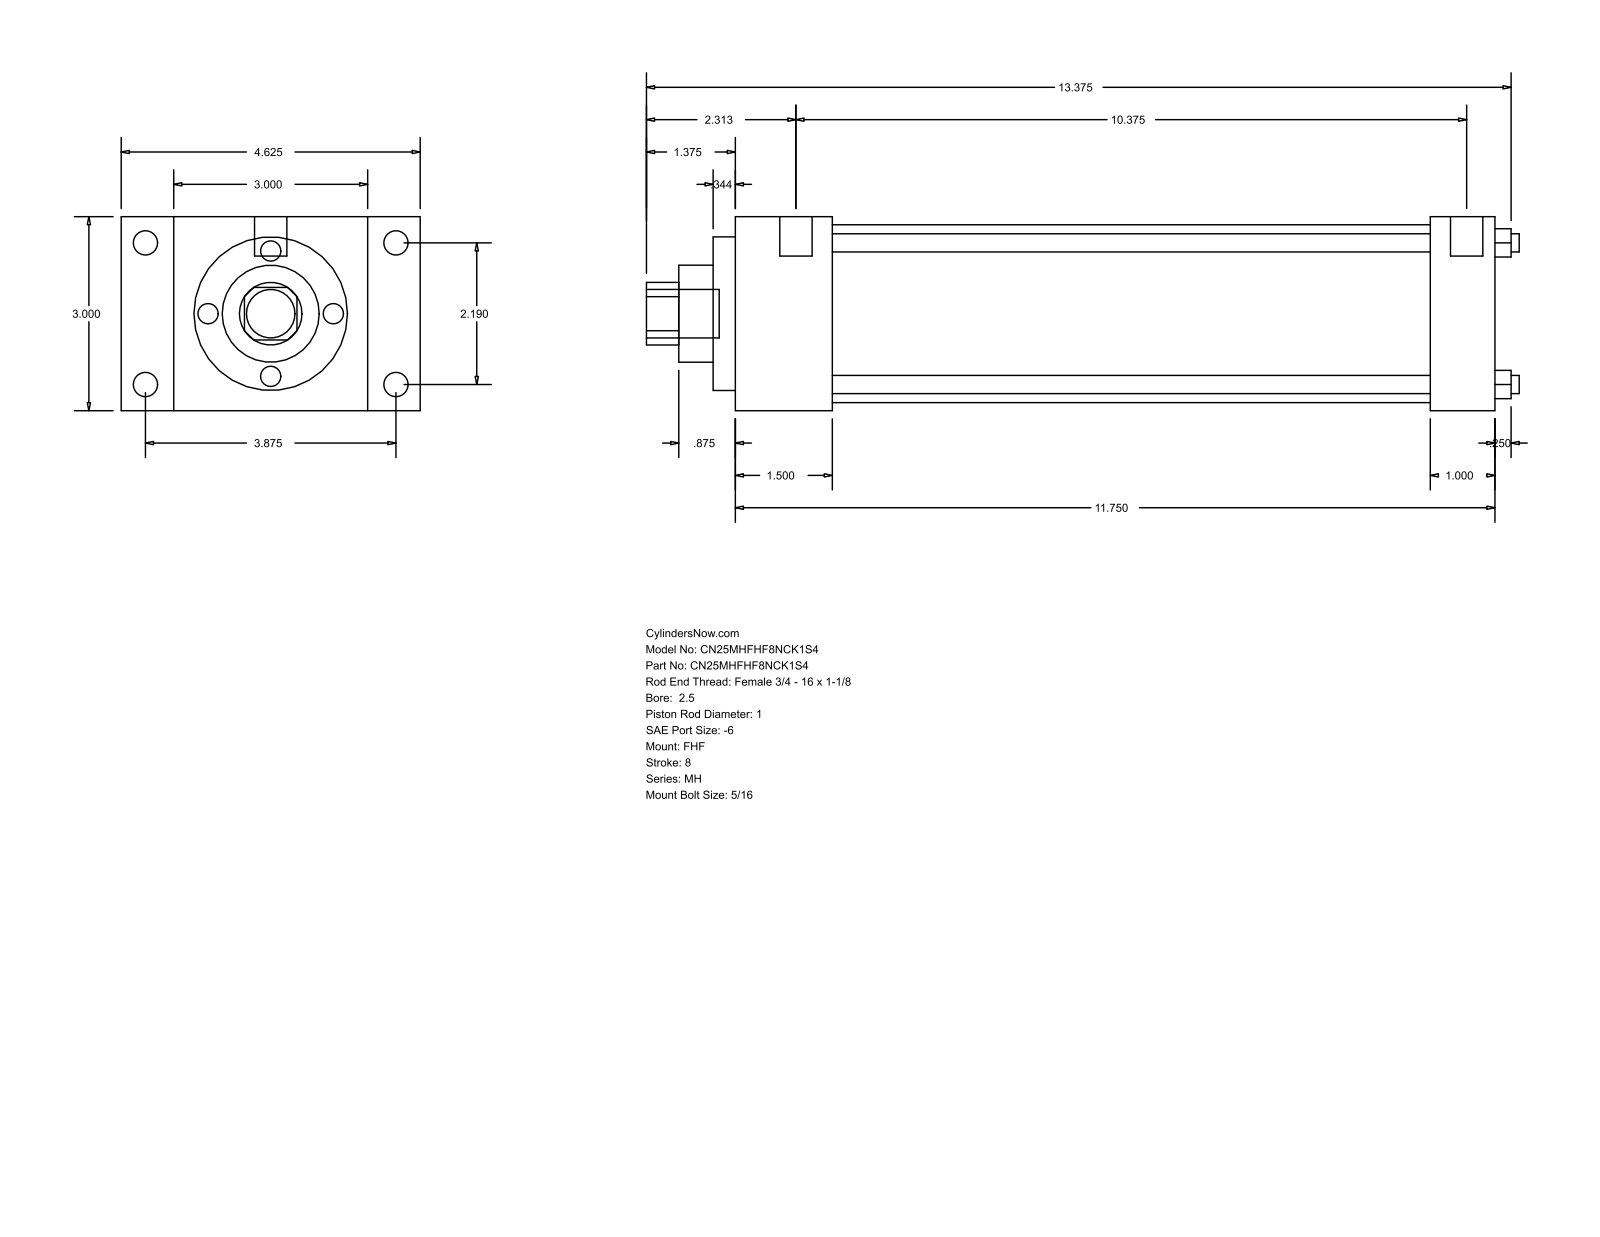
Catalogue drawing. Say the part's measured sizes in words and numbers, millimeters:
The part is named "MH_FHF__0250_1". Its 3-D file was written by "GSSL Pune (CONFIG_CONTROL_DESIGN)". It is 0 solids with 90 faces: 61 planar, 29 cylindrical and 0 other. Overall it measures 342.9 by 117.47 by 76.2 millimeters. Round holes: 4 of diameter 7.14, 1 of diameter 25.4, 1 of diameter 38.1, 1 of diameter 60.33, 1 of diameter 69.85. Round bosses or shafts: 4 of diameter 9.53, 4 of diameter 5.56, 2 of diameter 12.7, 1 of diameter 19.05. Partial cylindrical surfaces (rounded edges, fillets, slot ends): 1 of radius 12.29. The main face-to-face distances are 76.2, 298.46, 38.11, 260.35, 20.64, 96.84, 117.48, 273.06, 234.95, 25.4. The hole center spacings are 39.33, 55.62, 78.66.
